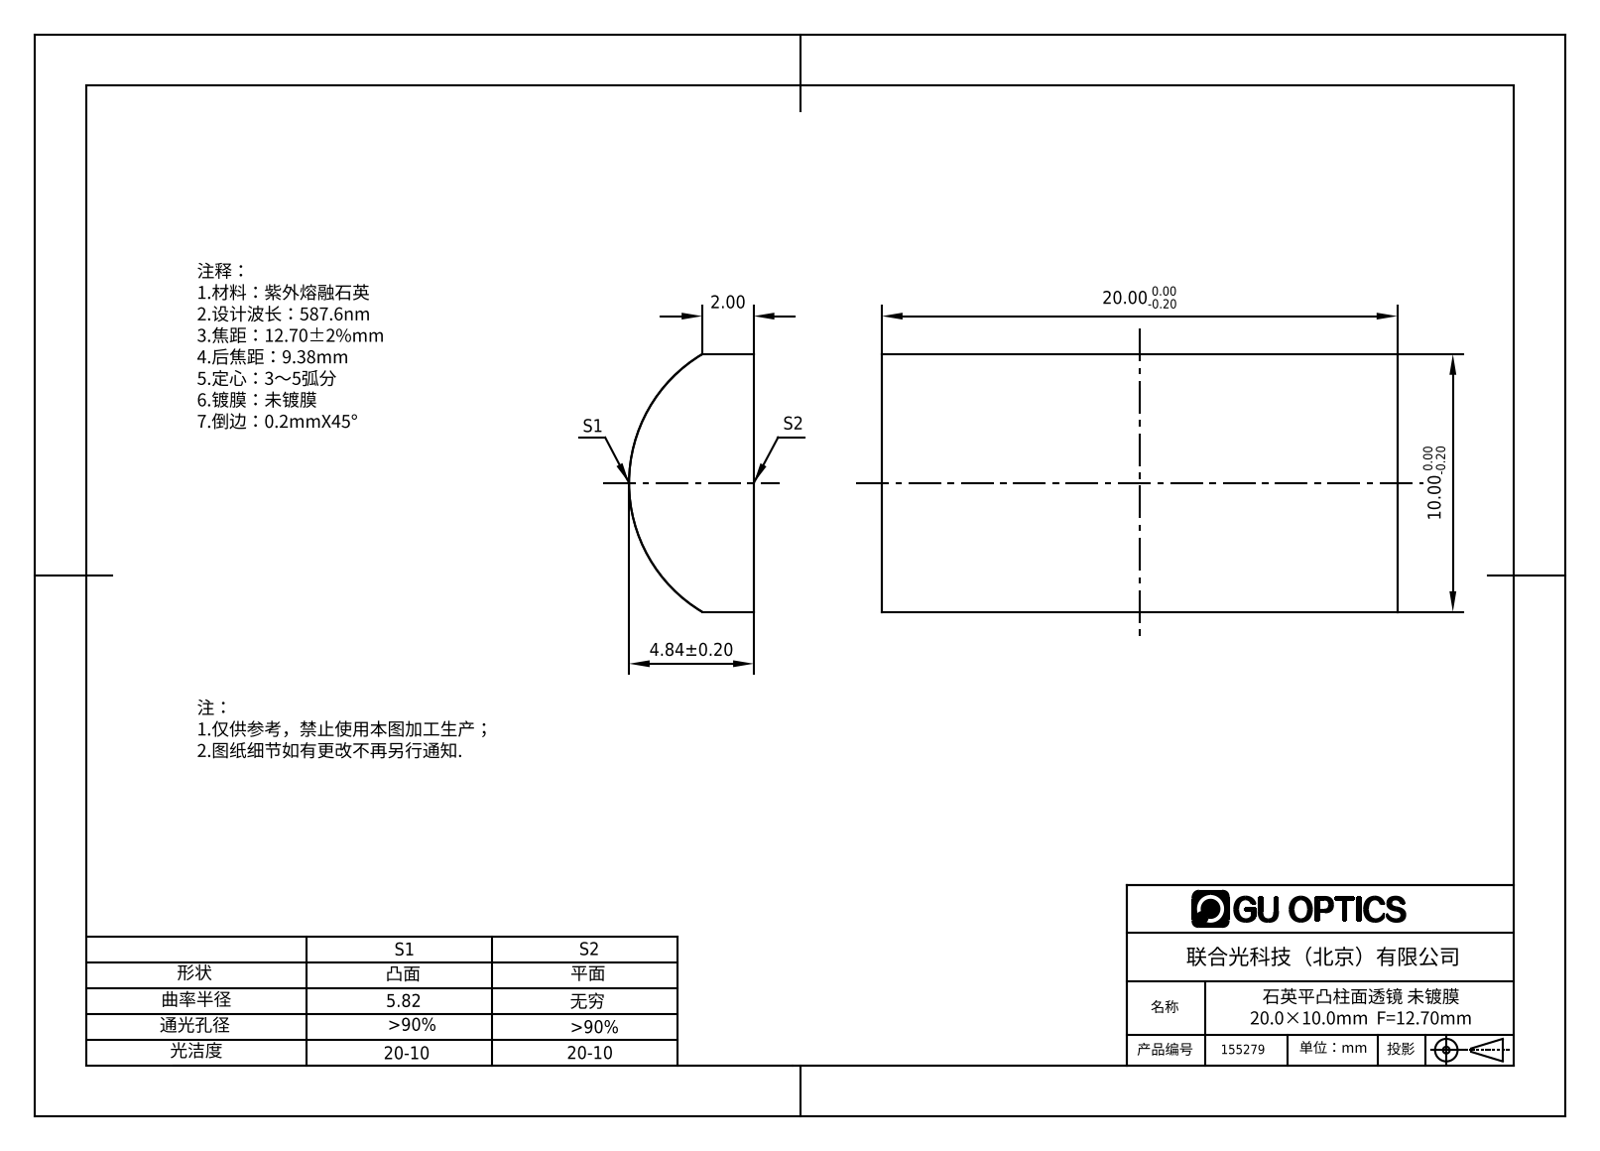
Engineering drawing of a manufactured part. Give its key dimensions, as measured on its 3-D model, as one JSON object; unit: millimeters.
{"part_name": "155279", "step_written_by": "SolidWorks 2016 (AUTOMOTIVE_DESIGN)", "units": "millimeters", "bodies": {"solids": 1, "faces": 6, "planar": 5, "cylindrical": 1, "other": 0}, "overall_size": [20, 10, 4.84], "volume_mm3": 802, "surface_area_mm2": 601, "partial_cylinders_radius": [[5.82, 1]], "face_to_face_distances": [20, 10]}
